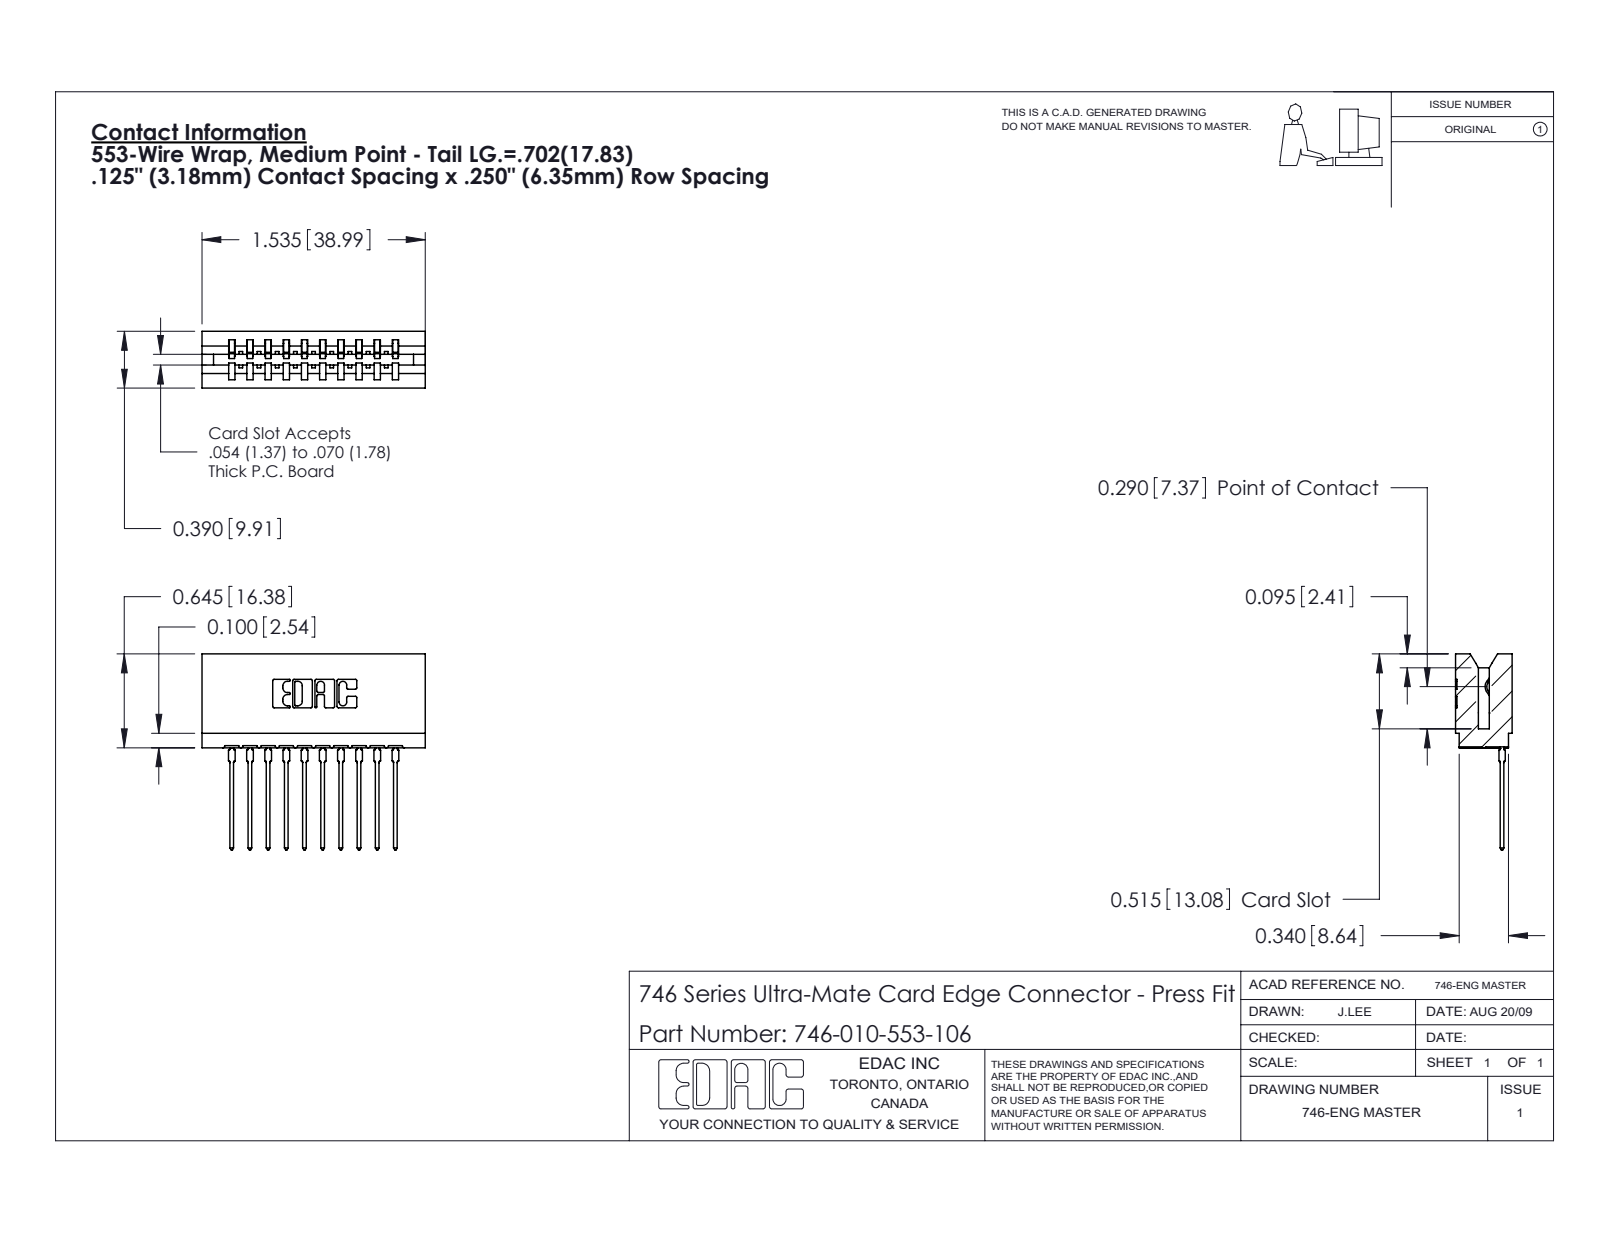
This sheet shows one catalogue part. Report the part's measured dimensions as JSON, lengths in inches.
{"part_name": "746 Part_.515 Slot Depth - 06; 746-292-001_553; 746-010-553-106", "step_written_by": "SolidWorks 2020 (CONFIG_CONTROL_DESIGN)", "units": "inches", "bodies": {"solids": 11, "faces": 1178, "planar": 686, "cylindrical": 232, "other": 260}, "overall_size": [1.535, 1.346, 0.39], "volume_in3": 0.263, "surface_area_in2": 9.373, "partial_cylinders_radius": [[0.01, 22], [0.021, 20], [0.015, 11], [0.007, 6], [0.031, 6], [0.005, 4], [0.011, 4], [0.026, 3]], "face_to_face_distances": [0.25, 0.333, 0.5, 0.057, 0.042, 0.125, 0.292, 0.75, 0.39, 0.375]}
